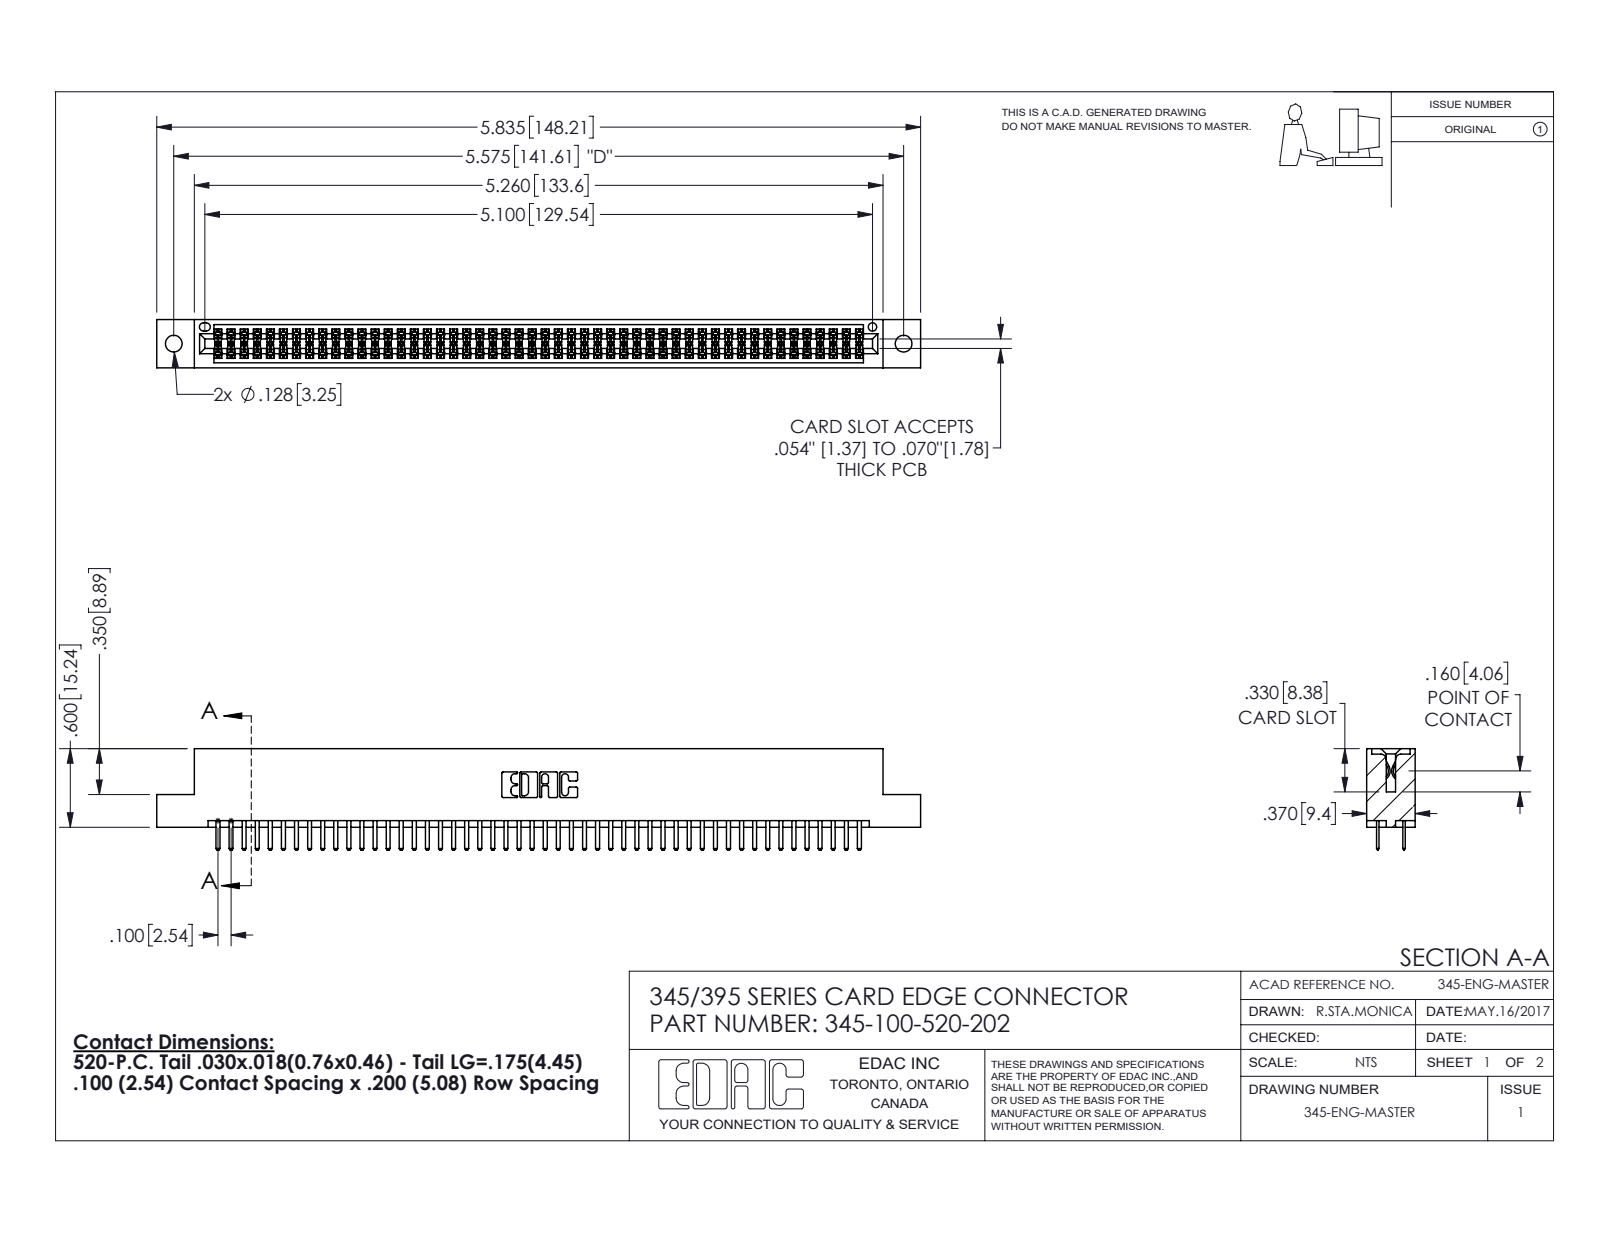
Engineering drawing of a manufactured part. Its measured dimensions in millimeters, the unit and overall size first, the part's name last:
Units: millimetres
Overall size (bounding box): 148.2 × 19.7 × 9.4
Round holes (diameter × count): ⌀3.3 ×2, ⌀1.6 ×1
Partial cylindrical surfaces — rounded edges, fillets, slot ends (radius × count): R0.2 ×150, R0.3 ×104, R0.3 ×22, R0.2 ×6, R0.8 ×6, R0.7 ×3, R0.4 ×2, R0.5 ×2
Main face-to-face distances: 7.6, 1.8, 5.1, 9.4, 2.5, 6.9, 0.6, 5.7, 0.6, 1.8
Hole centre spacings: 6.9, 135.6, 141.6
Volume: 14 400 mm³ · Surface area: 21 060 mm²
Bodies: 101 solids, 5526 faces (3580 planar, 1946 cylindrical, 0 other)
Part name (STEP PRODUCT): 345-292-001_345-293-120; 345 Part_Flush Mounting Lugs - 0.128 Dia; 345-100-520-202
STEP written by: SolidWorks 2016 (CONFIG_CONTROL_DESIGN)
